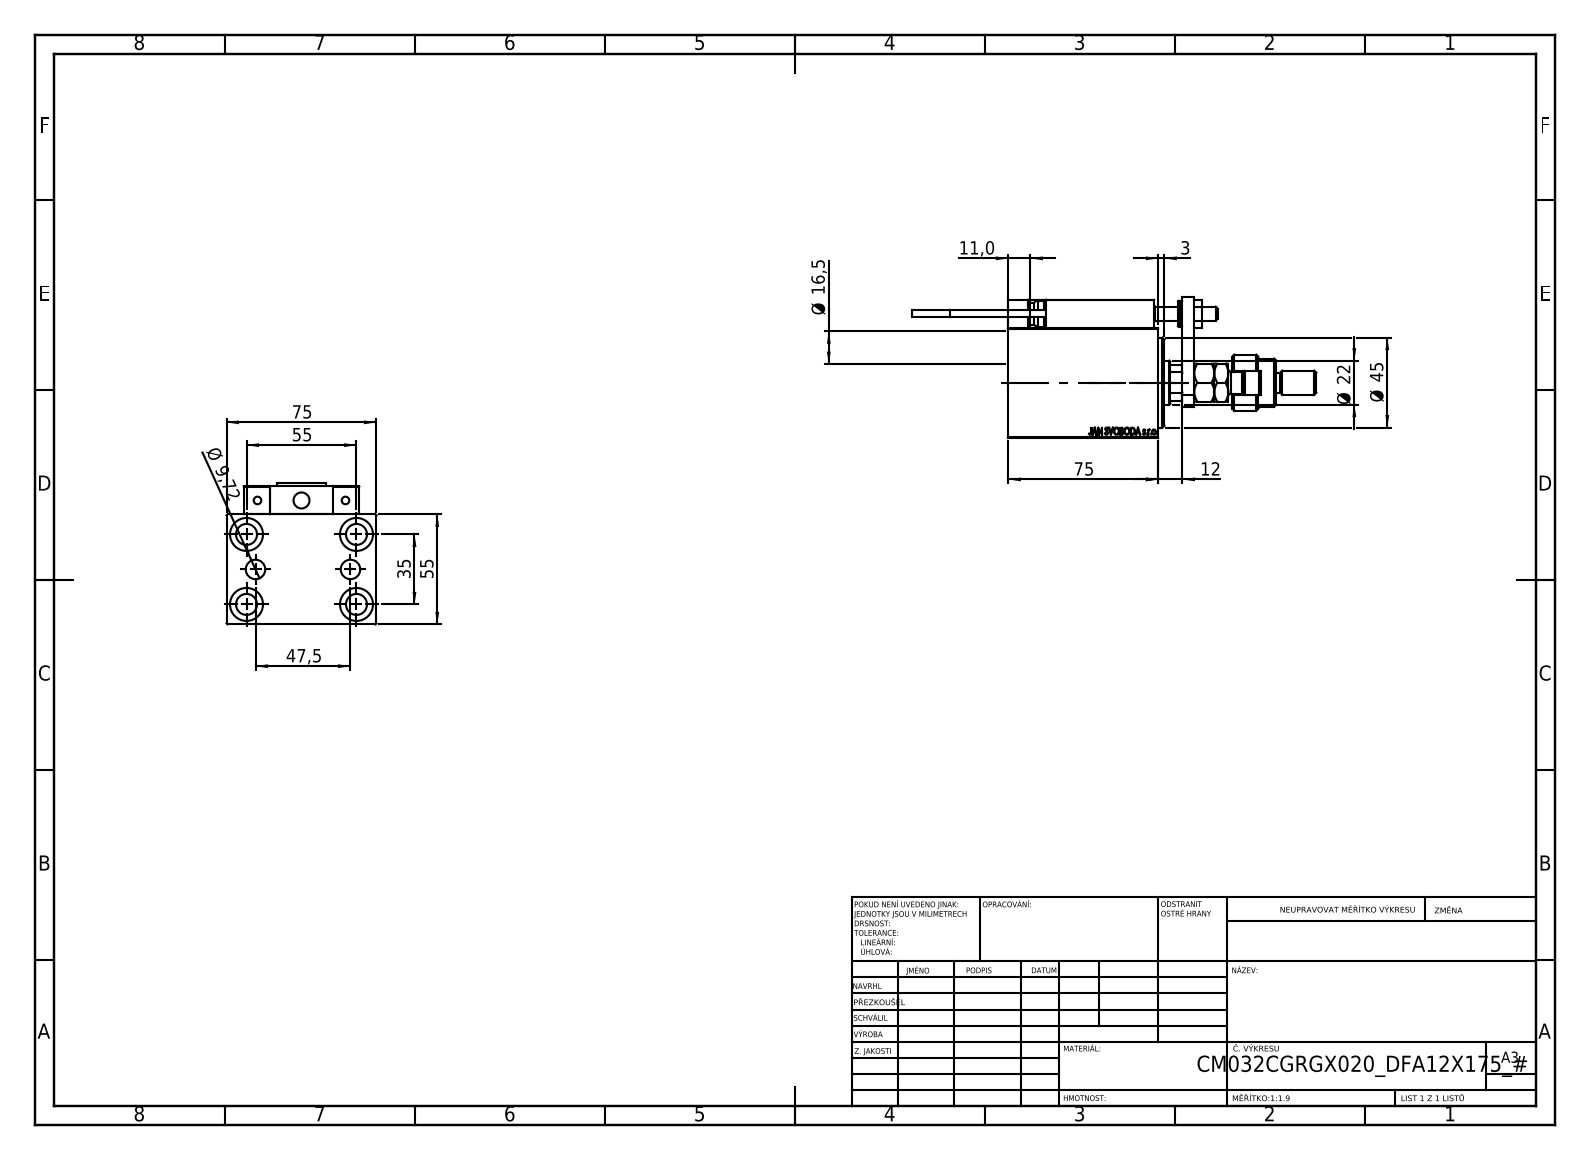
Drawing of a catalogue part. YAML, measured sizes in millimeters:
part_name: "ALLEN BOLT D5; V450CM_VC_B; ZARAZKA; SWITCH DIM B,W (+7 more)"
step_written_by: "SolidWorks 2019 (CONFIG_CONTROL_DESIGN)"
units: millimeters
bodies: {solids: 25, faces: 1357, planar: 586, cylindrical: 193, other: 578}
overall_size: [202, 75, 70.5]
volume: 333391
surface_area: 90987
round_holes:
  - {diameter: 8, count: 5}
  - {diameter: 10.5, count: 5}
  - {diameter: 16.5, count: 5}
  - {diameter: 3.2, count: 4}
  - {diameter: 4, count: 4}
  - {diameter: 5, count: 2}
  - {diameter: 9.72, count: 2}
  - {diameter: 7, count: 1}
  - {diameter: 22, count: 1}
  - {diameter: 25.5, count: 1}
  - {diameter: 32, count: 1}
  - {diameter: 34, count: 1}
round_bosses_or_shafts:
  - {diameter: 11, count: 2}
  - {diameter: 5, count: 2}
  - {diameter: 3.8, count: 2}
  - {diameter: 28, count: 1}
  - {diameter: 24, count: 1}
  - {diameter: 18, count: 1}
  - {diameter: 13, count: 1}
  - {diameter: 12, count: 1}
partial_cylinders:
  - {radius: 0.3, count: 30}
  - {radius: 3, count: 2}
  - {radius: 9.75, count: 1}
  - {radius: 10.5, count: 1}
face_to_face_distances: [55, 75, 14, 10, 12, 69, 18, 25, 7, 6]
hole_center_spacings: [32.6, 11.37, 17.76, 18.07, 20, 27.07, 29.59, 29.69]
